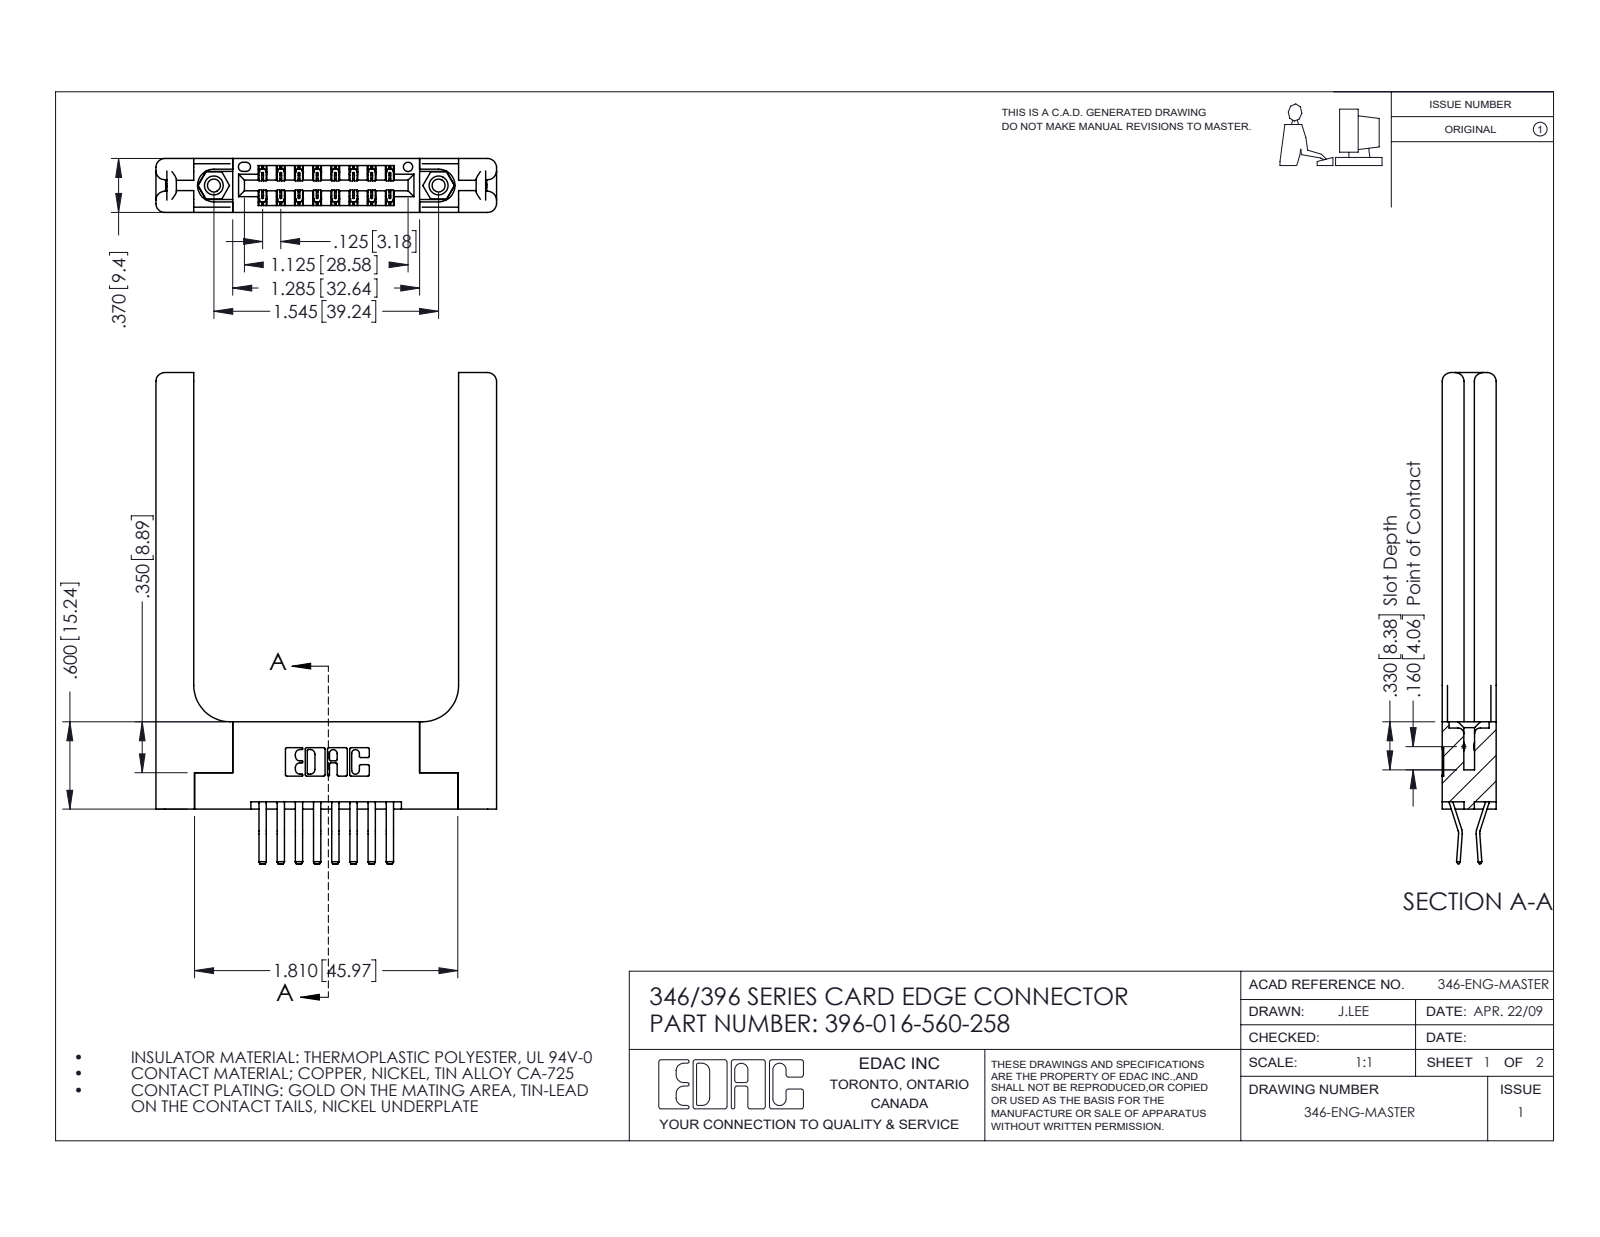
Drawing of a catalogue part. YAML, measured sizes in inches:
part_name: "345-250-001_345-250-001-102; 396-016-560-258; 346-220-058_345-220-058; 346 Part_Flush Mounting Lugs - 0.156 Dia-TH (+1 more)"
step_written_by: "SolidWorks 2016 (CONFIG_CONTROL_DESIGN)"
units: inches
bodies: {solids: 21, faces: 1242, planar: 784, cylindrical: 398, other: 60}
overall_size: [3.375, 2.341, 0.37]
volume: 0.801
surface_area: 19.33
round_holes:
  - {diameter: 0.089, count: 2}
  - {diameter: 0.125, count: 2}
  - {diameter: 0.156, count: 2}
  - {diameter: 0.064, count: 1}
round_bosses_or_shafts:
  - {diameter: 0.155, count: 2}
partial_cylinders:
  - {radius: 0.006, count: 24}
  - {radius: 0.01, count: 22}
  - {radius: 0.06, count: 16}
  - {radius: 0.007, count: 6}
  - {radius: 0.031, count: 6}
  - {radius: 0.026, count: 3}
  - {radius: 0.01, count: 2}
  - {radius: 0.014, count: 2}
face_to_face_distances: [0.37, 0.15, 0.22, 0.072, 0.148, 0.25, 0.102, 0.048, 0.322, 0.173]
hole_center_spacings: [0.246, 1.341, 1.545]
